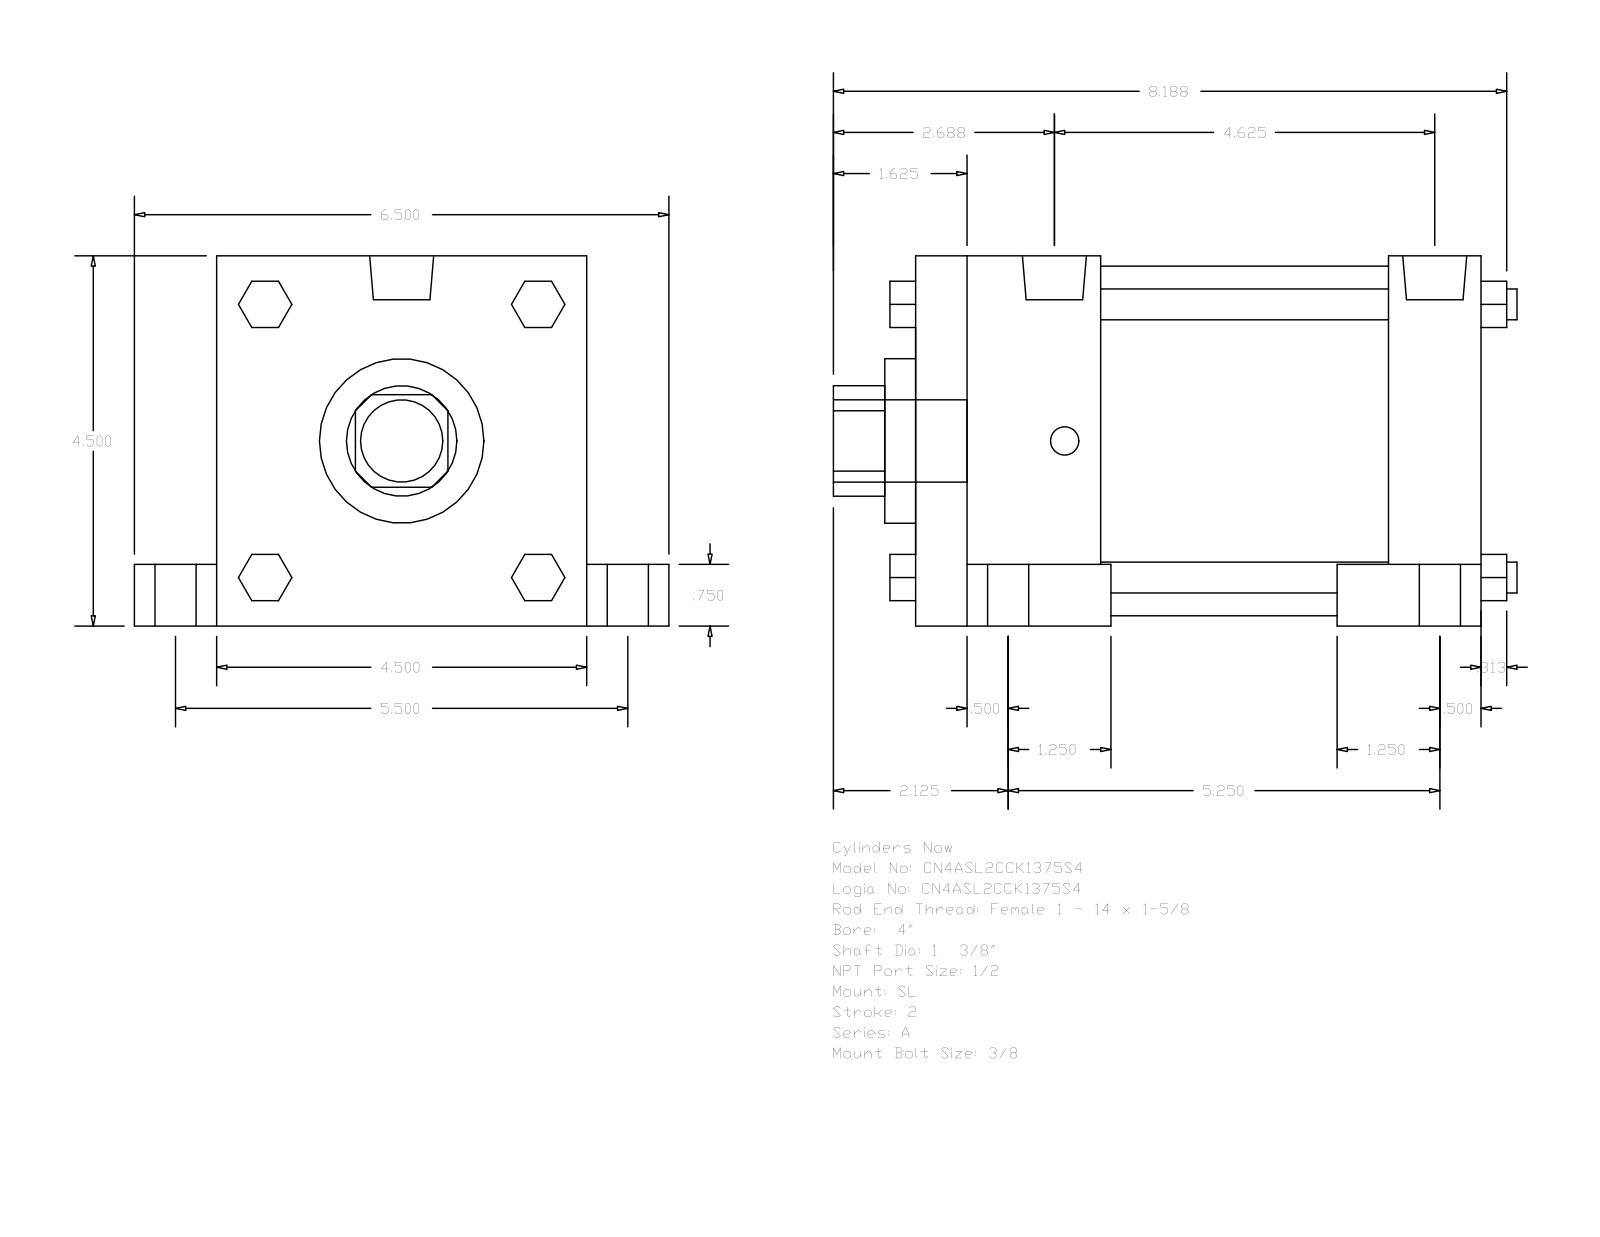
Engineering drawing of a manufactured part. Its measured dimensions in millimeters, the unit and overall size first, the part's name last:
Units: millimetres
Overall size (bounding box): 211.14 × 165.1 × 114.3
Round holes (diameter × count): ⌀34.92 ×1, ⌀50.8 ×1, ⌀107.95 ×1
Round bosses / shafts (diameter × count): ⌀19.05 ×4, ⌀12.7 ×4, ⌀9.53 ×4, ⌀8.73 ×4, ⌀19.77 ×2, ⌀25.4 ×1
Partial cylindrical surfaces — rounded edges, fillets, slot ends (radius × count): R17.06 ×1
Main face-to-face distances: 114.3, 174.63, 28.58, 25.4, 57.15, 117.48, 146.05, 88.9, 139.7, 19.05
Bodies: 0 solids, 150 faces (114 planar, 36 cylindrical, 0 other)
Part name (STEP PRODUCT): A_SL__0400_1.375
STEP written by: GSSL Pune (CONFIG_CONTROL_DESIGN)
